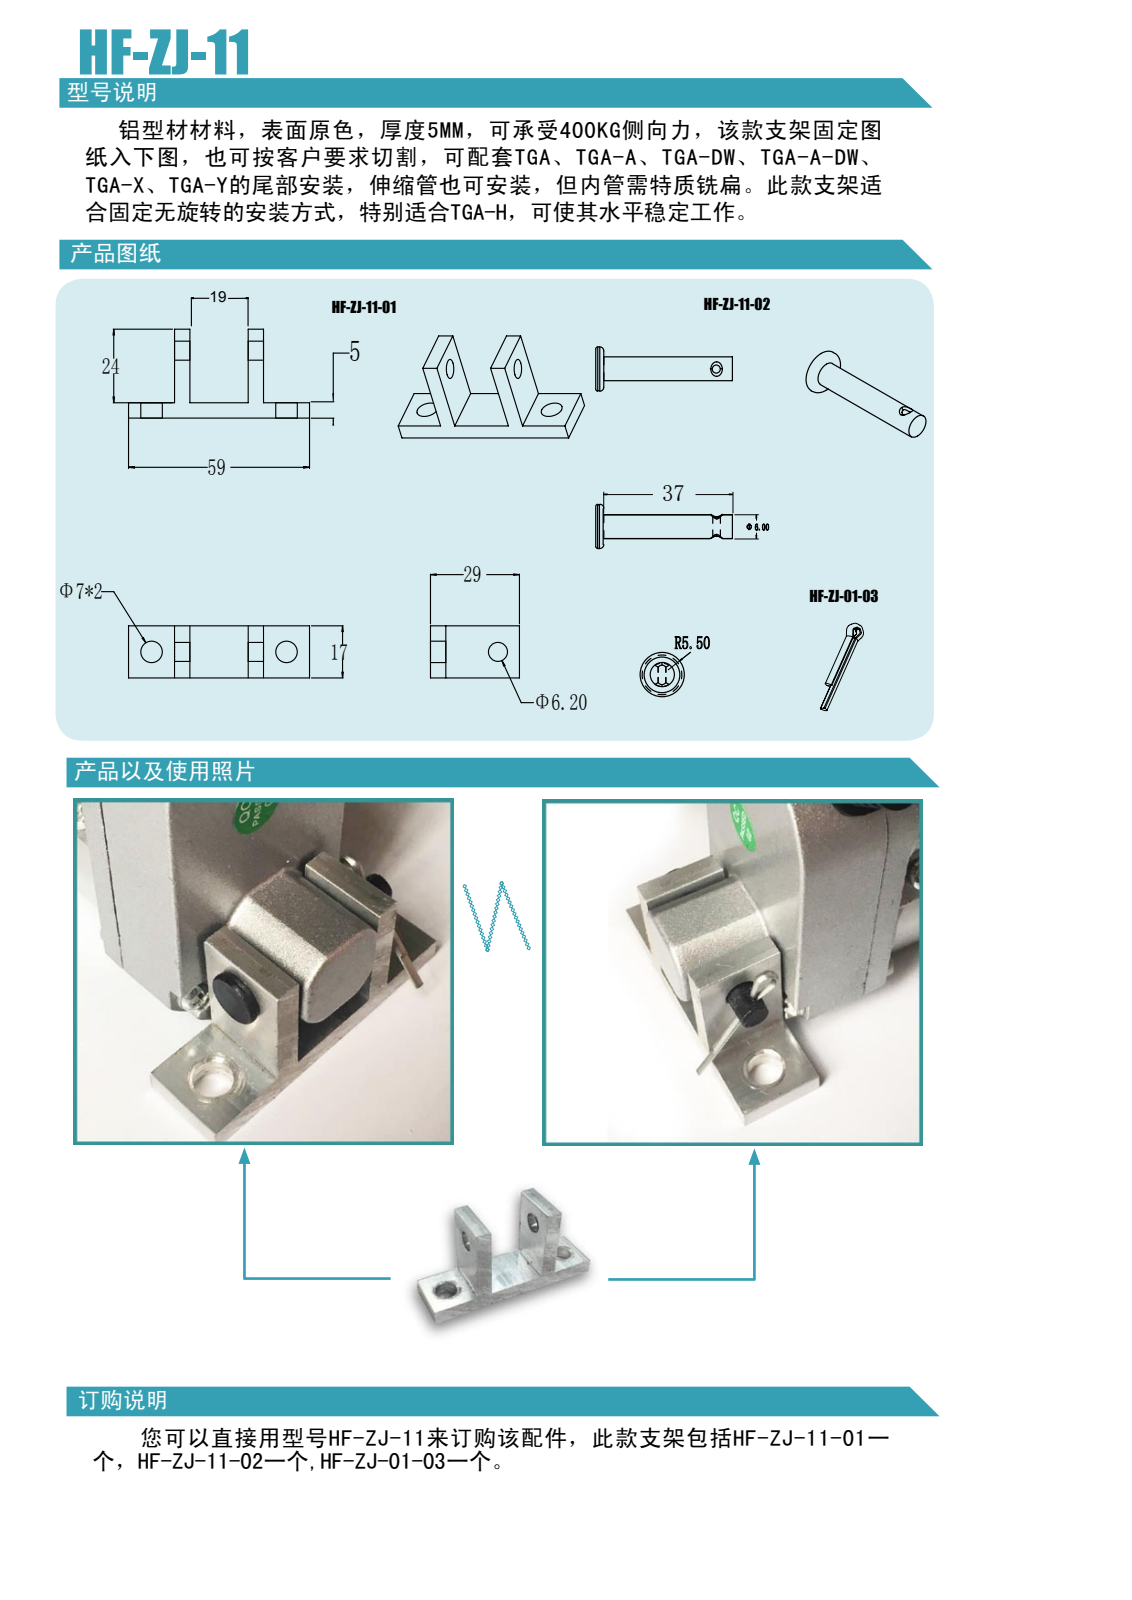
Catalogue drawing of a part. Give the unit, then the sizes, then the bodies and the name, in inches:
Units: inches
Overall size (bounding box): 2.323 × 1.142 × 0.669
Round holes (diameter × count): ⌀0.276 ×2, ⌀0.244 ×1
Main face-to-face distances: 0.197, 0.945, 1.142, 0.669, 0.748, 0.591, 0.787, 1.535, 1.732, 2.323
Hole centre spacings: 1.732
Volume: 0.513 in³ · Surface area: 7.778 in²
Bodies: 1 solid, 22 faces (14 planar, 8 cylindrical, 0 other)
Part name (STEP PRODUCT): ZJ-11
STEP written by: PRO/ENGINEER BY PARAMETRIC TECHNOLOGY CORPORATION, 2008380 (CONFIG_CONTROL_DESIGN)
